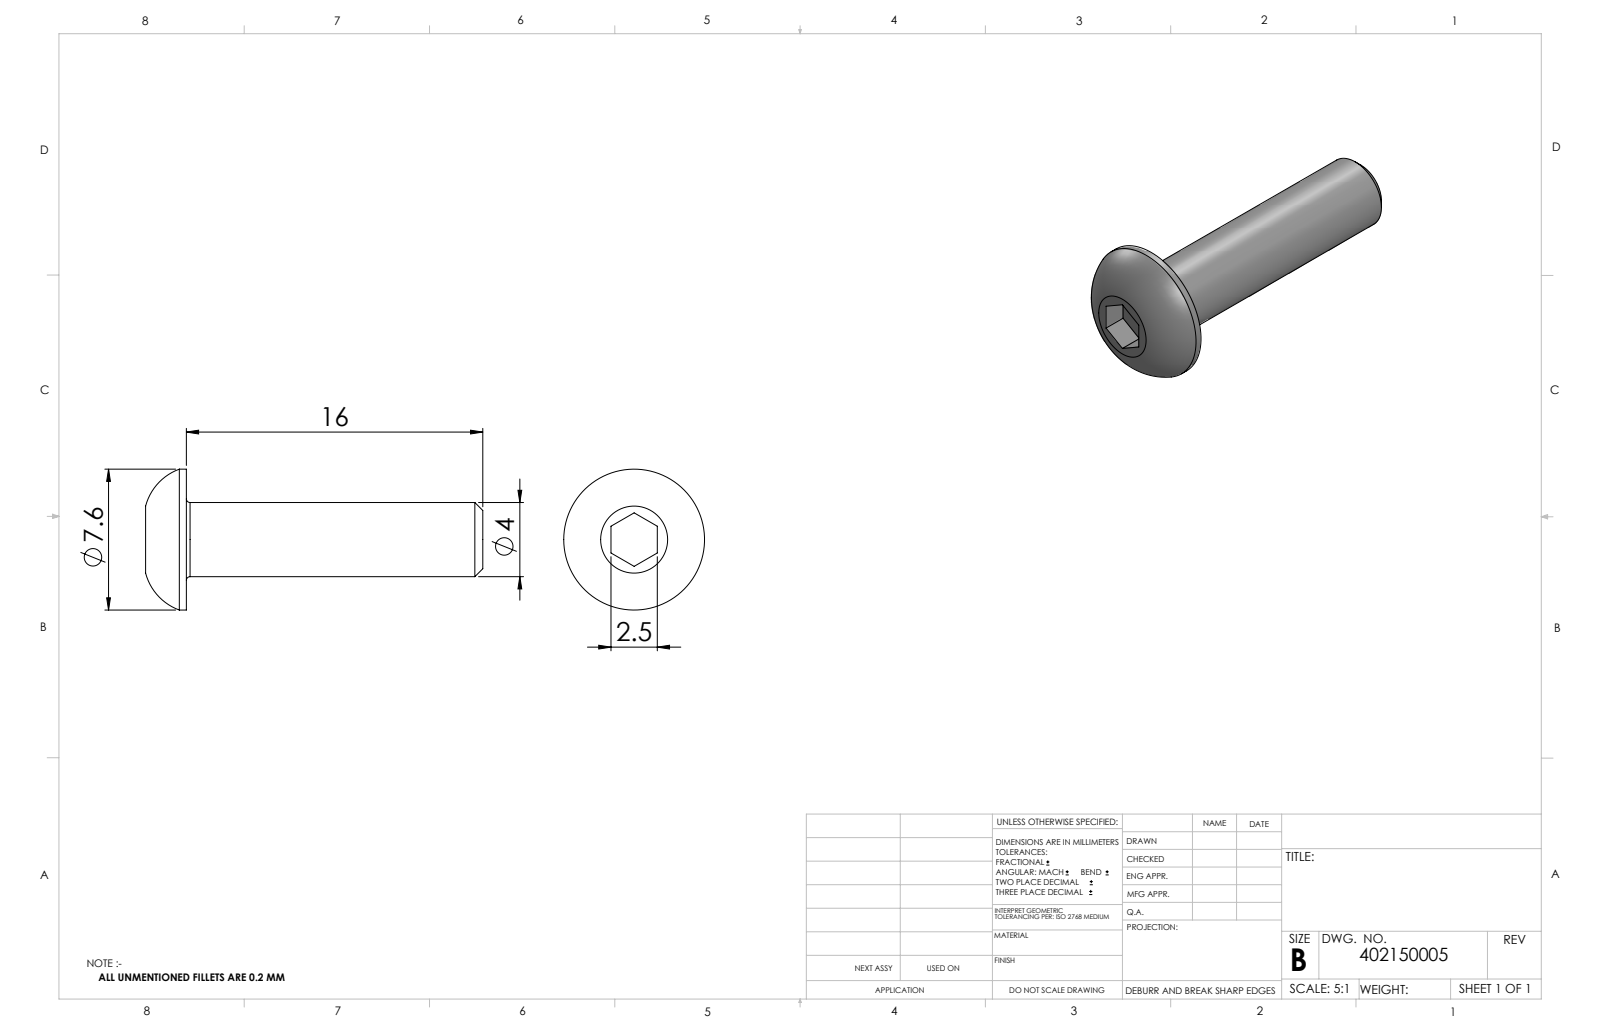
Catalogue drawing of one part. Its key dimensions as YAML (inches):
part_name: "402150005_c_1"
step_written_by: "SolidWorks 2014 (CONFIG_CONTROL_DESIGN)"
units: inches
bodies: {solids: 1, faces: 20, planar: 10, cylindrical: 4, other: 6}
overall_size: [0.717, 0.299, 0.299]
volume: 0.016
surface_area: 0.504
round_bosses_or_shafts:
  - {diameter: 0.299, count: 1}
  - {diameter: 0.157, count: 1}
face_to_face_distances: [0.63, 0.098, 0.665, 0.035, 0.717, 0.087, 0.051]
